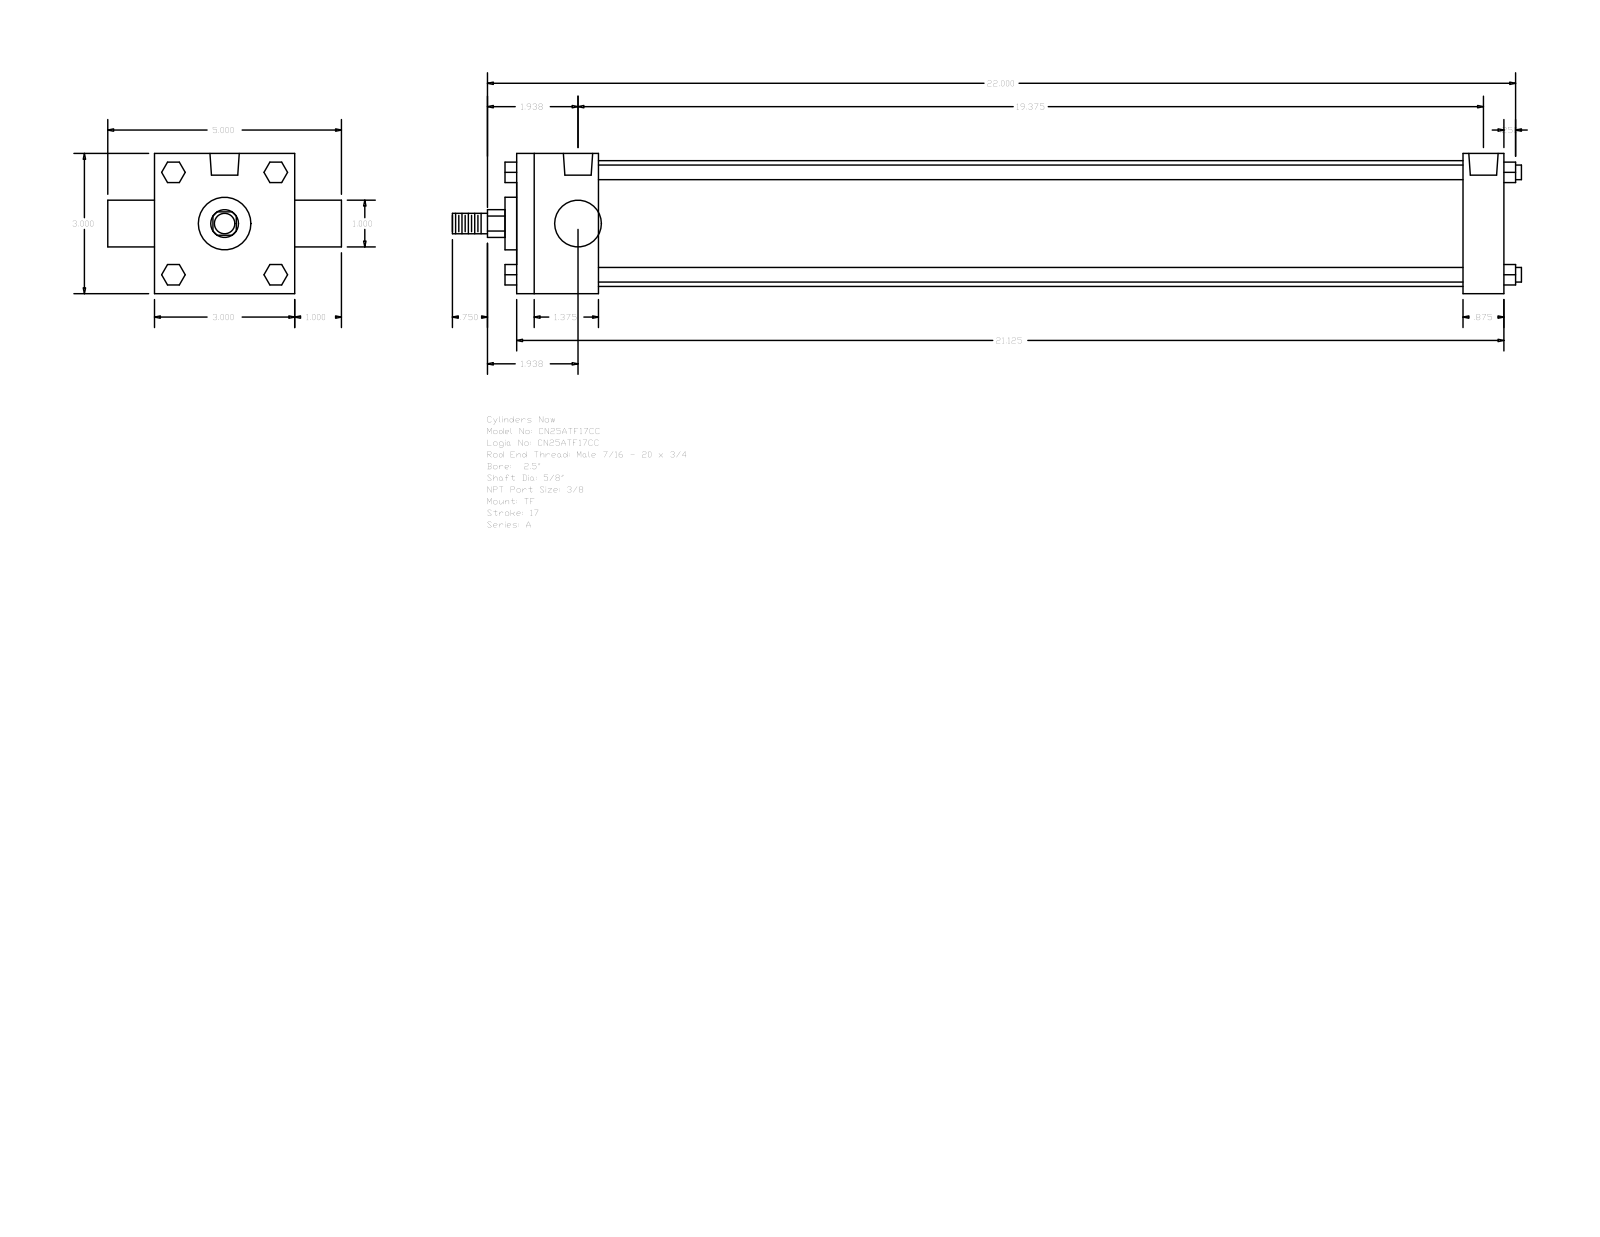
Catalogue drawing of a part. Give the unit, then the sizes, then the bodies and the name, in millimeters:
Units: millimetres
Overall size (bounding box): 581.02 × 127 × 76.2
Round holes (diameter × count): ⌀5.56 ×3, ⌀15.93 ×2
Round bosses / shafts (diameter × count): ⌀7.94 ×4, ⌀68.33 ×1, ⌀28.57 ×1, ⌀25.4 ×1, ⌀15.88 ×1, ⌀11.11 ×1
Partial cylindrical surfaces — rounded edges, fillets, slot ends (radius × count): R7.54 ×1
Main face-to-face distances: 76.2, 536.57, 44.45, 514.35, 469.9, 492.12, 22.22, 25.4, 101.6, 6.35
Hole centre spacings: 2.38, 494.51, 492.13, 496.89
Bodies: 0 solids, 120 faces (92 planar, 28 cylindrical, 0 other)
Part name (STEP PRODUCT): A_TF__0250_0.625
STEP written by: GSSL Pune (CONFIG_CONTROL_DESIGN)
